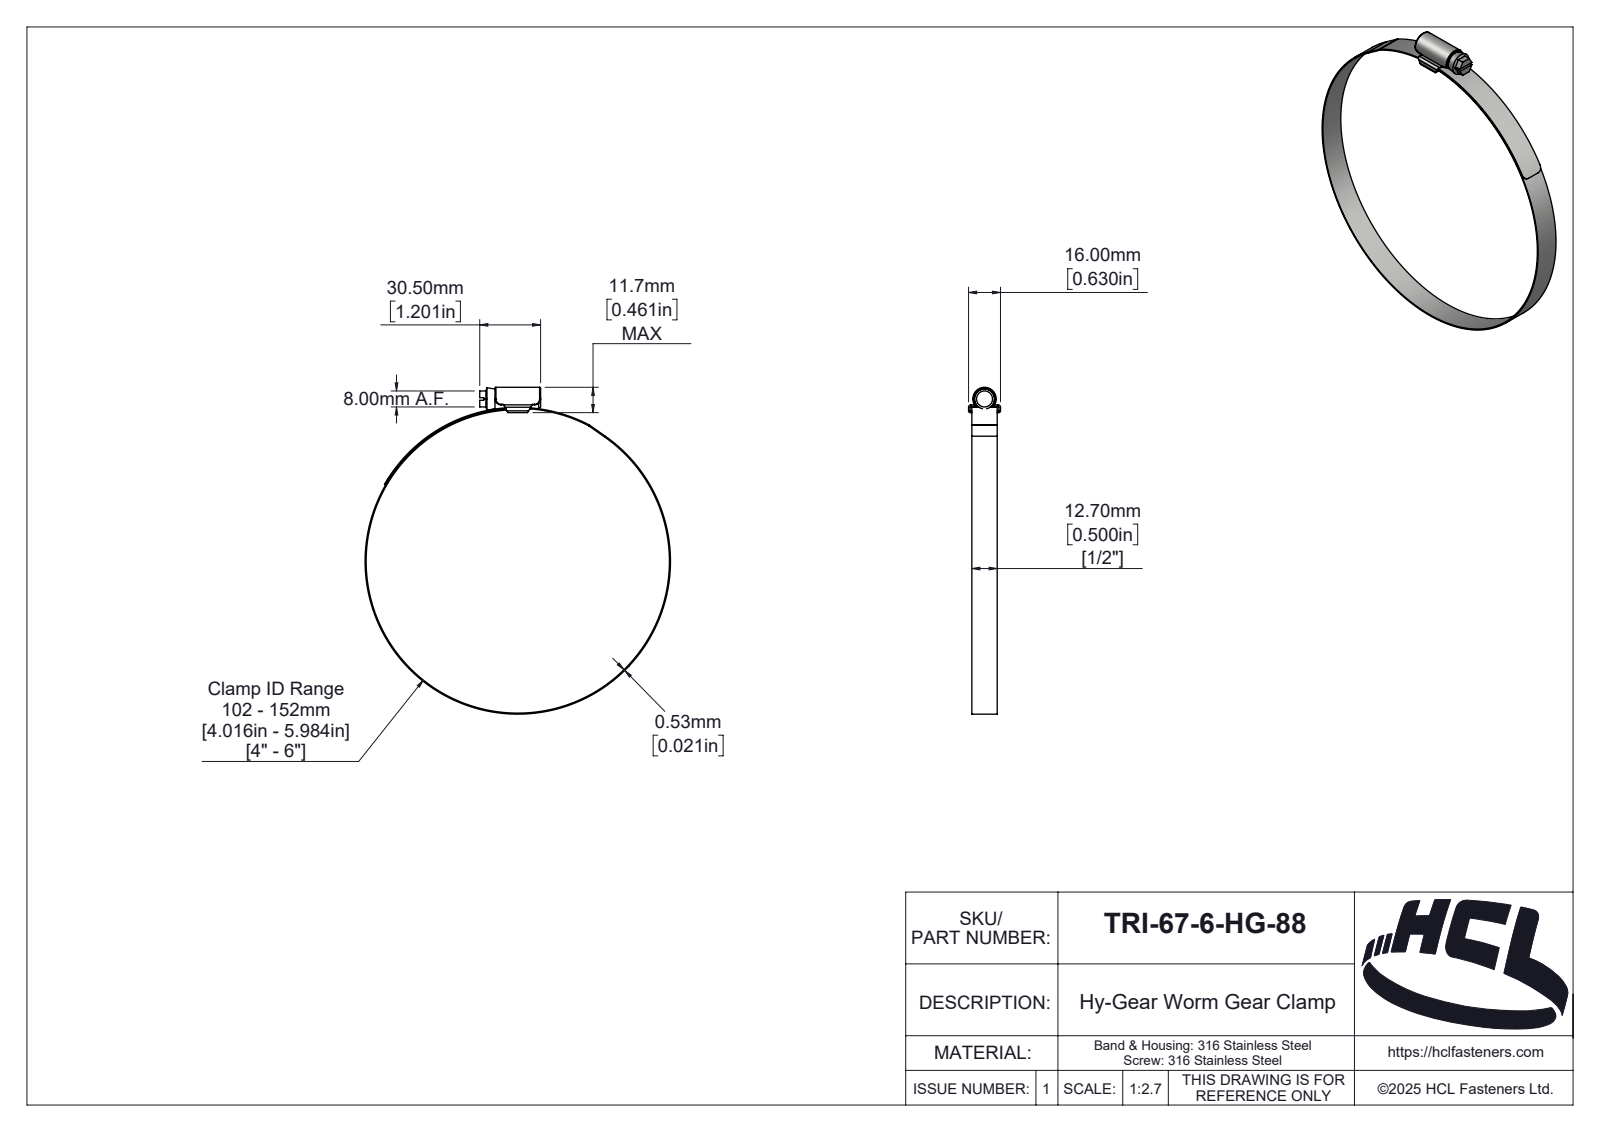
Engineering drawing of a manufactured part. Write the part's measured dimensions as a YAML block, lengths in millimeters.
part_name: "TRI-57-0-HG-88"
step_written_by: "SolidWorks 2025 (AUTOMOTIVE_DESIGN)"
units: millimeters
bodies: {solids: 3, faces: 189, planar: 39, cylindrical: 89, other: 61}
overall_size: [163.73, 153.06, 16]
volume: 6760
surface_area: 17723
round_holes:
  - {diameter: 152, count: 1}
round_bosses_or_shafts:
  - {diameter: 153.06, count: 1}
  - {diameter: 10, count: 1}
partial_cylinders:
  - {radius: 0.5, count: 6}
  - {radius: 3, count: 4}
  - {radius: 0.1, count: 2}
  - {radius: 0.9, count: 2}
  - {radius: 1.2, count: 2}
  - {radius: 0.46, count: 1}
  - {radius: 1.89, count: 1}
  - {radius: 2, count: 1}
face_to_face_distances: [12.7, 0.8, 3.1, 0.53, 2.3, 3.9, 30.5, 1.65, 14.35, 15.2]
